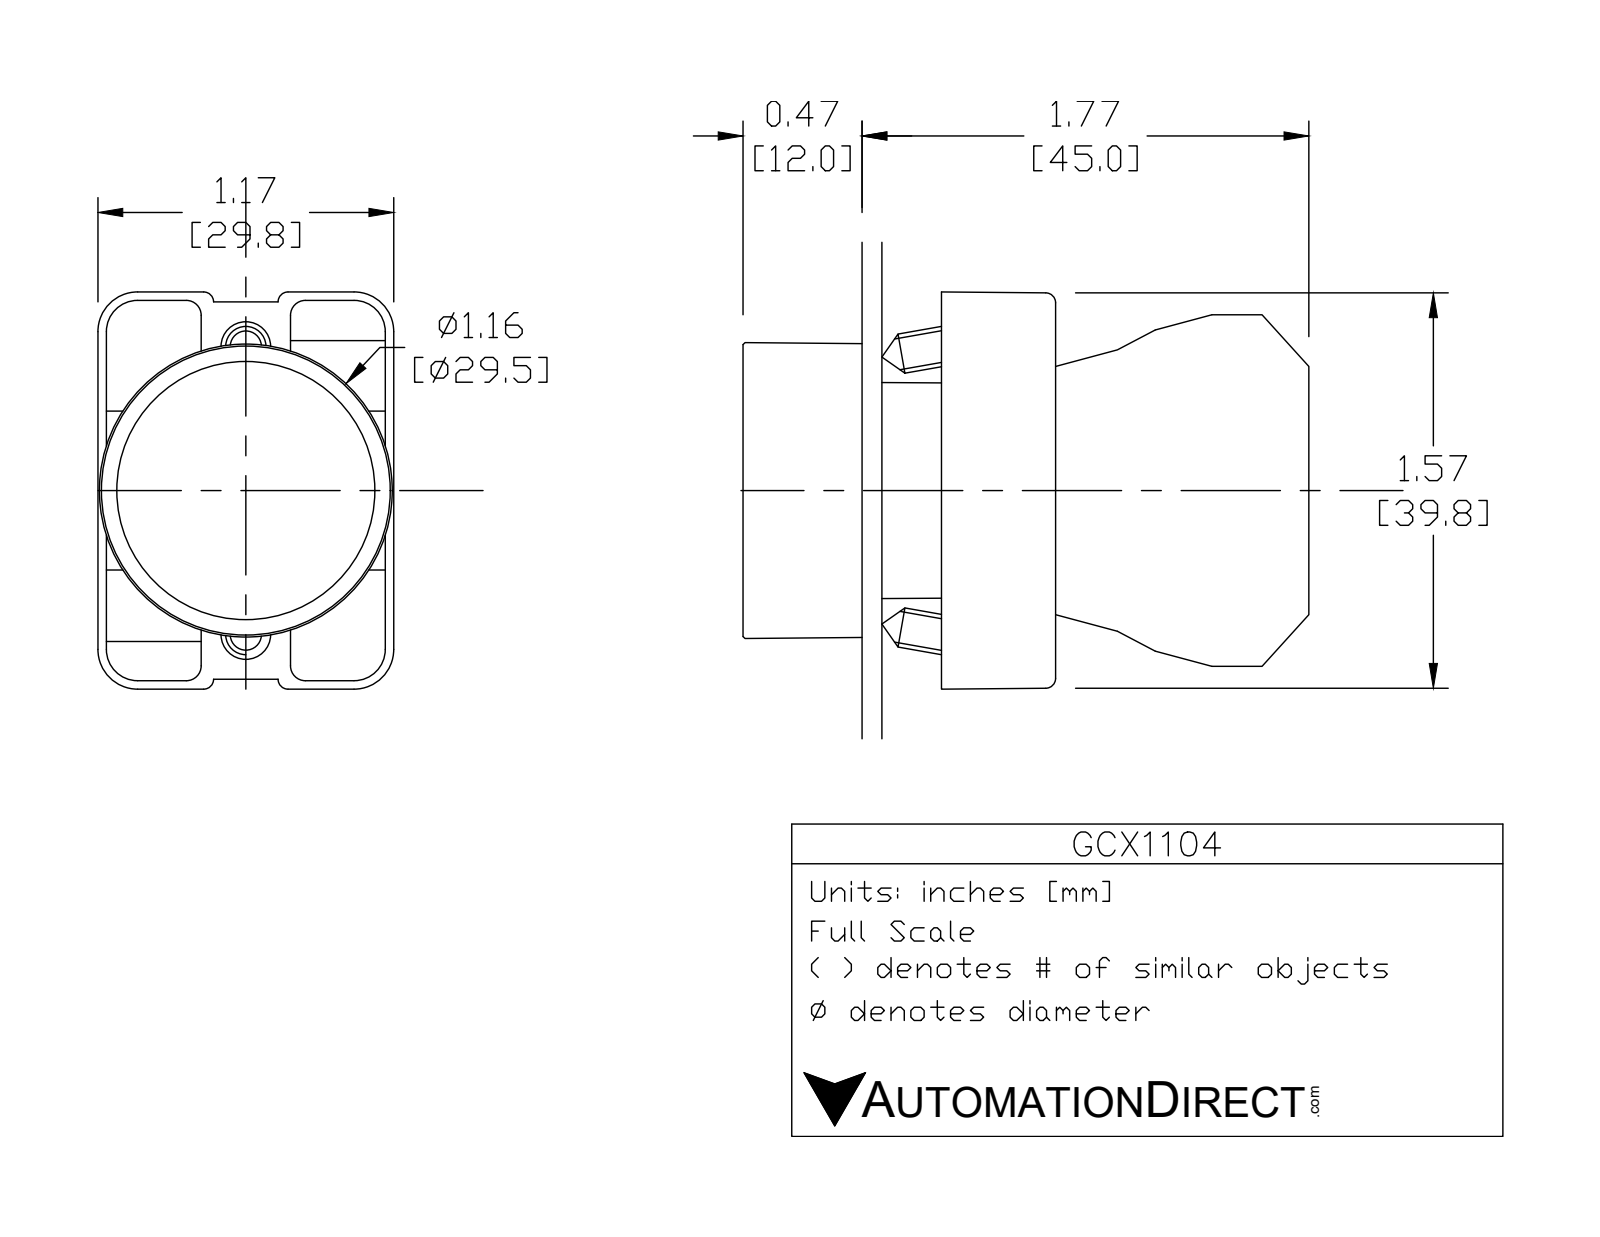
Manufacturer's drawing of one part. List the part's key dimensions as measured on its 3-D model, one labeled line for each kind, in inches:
Part name (STEP PRODUCT): ecx1029; ecx1040; GCX1104 OPERATOR; GCX1104
STEP written by: SolidWorks 2016 (AUTOMOTIVE_DESIGN)
Units: inches
Bodies: 6 solids, 381 faces (222 planar, 132 cylindrical, 27 other)
Overall size (bounding box): 2.217 × 1.581 × 1.177
Volume: 1.741 in³ · Surface area: 27.14 in²
Round holes (diameter × count): ⌀0.079 ×2, ⌀0.124 ×2, ⌀0.13 ×2, ⌀0.087 ×1, ⌀0.197 ×1, ⌀0.878 ×1, ⌀0.888 ×1, ⌀1.024 ×1
Round bosses / shafts (diameter × count): ⌀0.157 ×2, ⌀1.175 ×1, ⌀1.004 ×1, ⌀0.945 ×1, ⌀0.856 ×1, ⌀0.78 ×1
Partial cylindrical surfaces — rounded edges, fillets, slot ends (radius × count): R0.059 ×24, R0.041 ×12, R0.124 ×12, R0.157 ×12, R0.039 ×4, R0.128 ×2, R0.02 ×1, R0.063 ×1
Main face-to-face distances: 0.72, 0.579, 0.033, 0.472, 1.193, 0.031, 0.689, 0.598, 1.161, 1.071
Hole centre spacings: 0.236, 0.544, 0.472, 0.49
